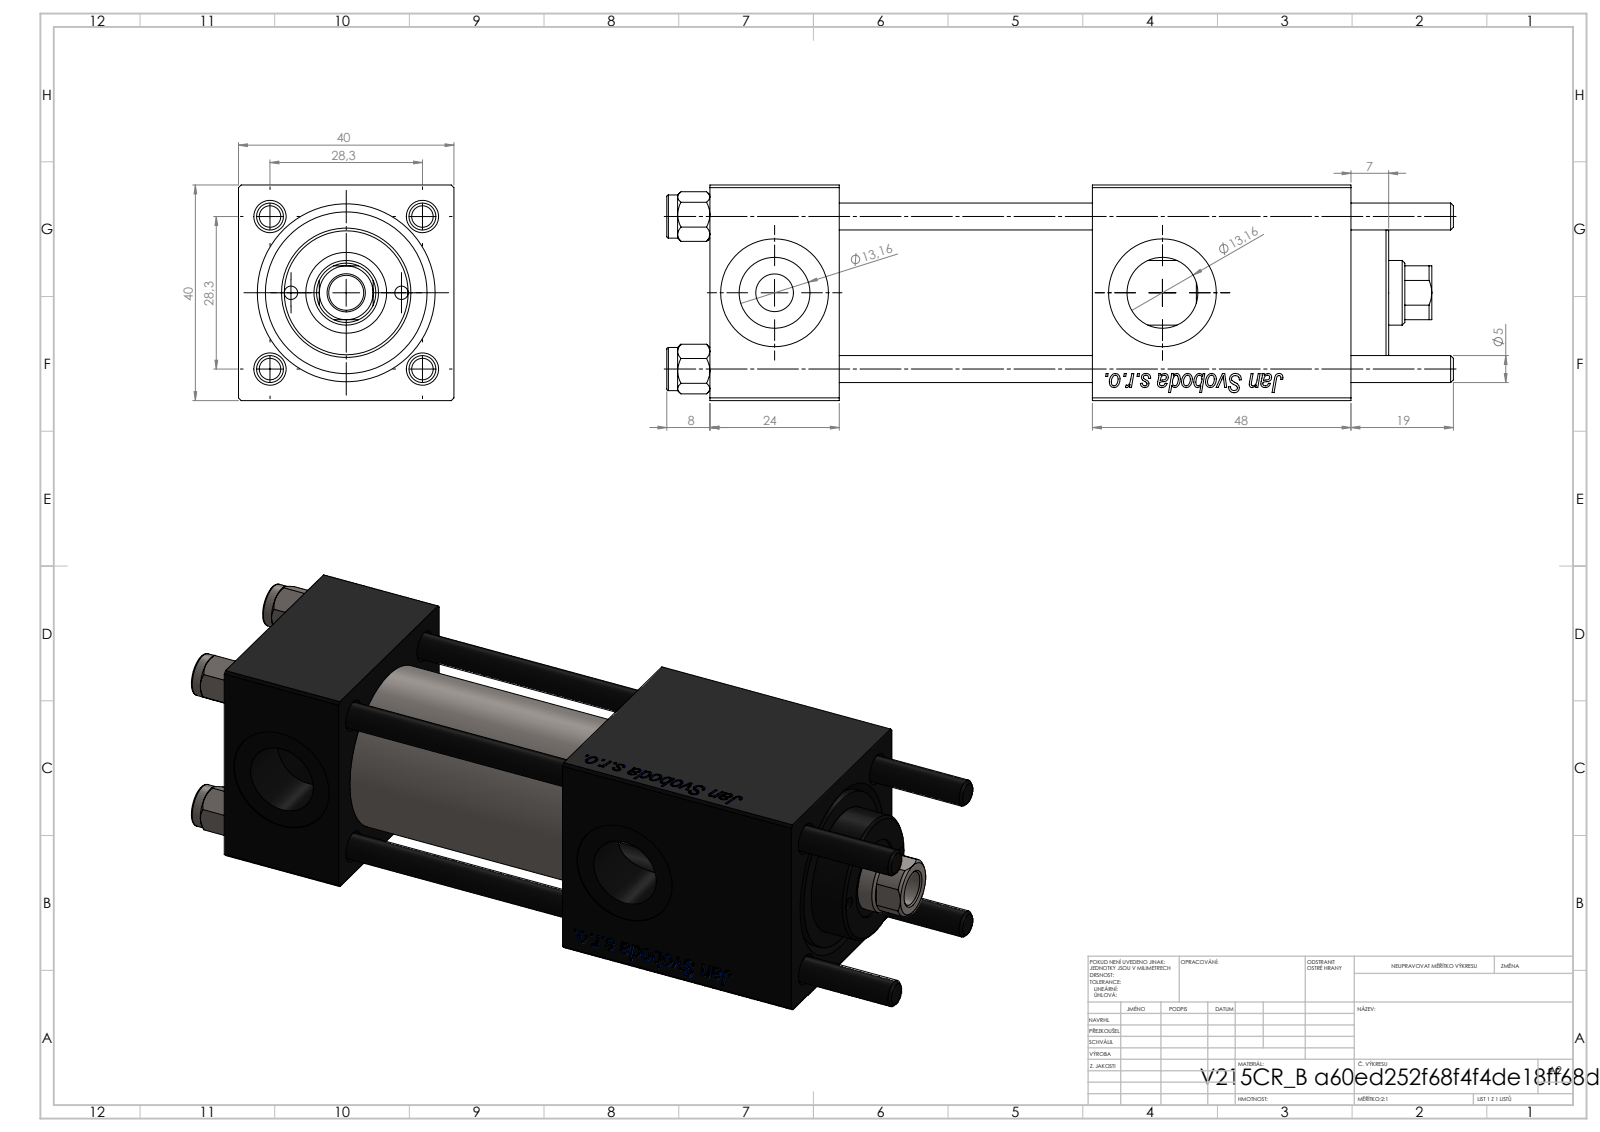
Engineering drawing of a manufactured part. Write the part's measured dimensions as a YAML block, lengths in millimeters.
part_name: "V215CR_B-1; V215_VC_A; V215CR_VCP_B; NUT_M5_B (+1 more)"
step_written_by: "SolidWorks 2019 (CONFIG_CONTROL_DESIGN)"
units: millimeters
bodies: {solids: 11, faces: 1161, planar: 431, cylindrical: 82, other: 648}
overall_size: [146, 40, 40]
volume: 144766
surface_area: 58808
round_holes:
  - {diameter: 5, count: 4}
  - {diameter: 20, count: 3}
  - {diameter: 2.5, count: 2}
  - {diameter: 7, count: 2}
  - {diameter: 13.16, count: 2}
  - {diameter: 6.5, count: 1}
  - {diameter: 12, count: 1}
  - {diameter: 15, count: 1}
  - {diameter: 25, count: 1}
  - {diameter: 30, count: 1}
round_bosses_or_shafts:
  - {diameter: 8, count: 4}
  - {diameter: 31, count: 1}
  - {diameter: 24, count: 1}
partial_cylinders:
  - {radius: 5.5, count: 1}
face_to_face_distances: [40, 24, 90.3, 66.3, 71, 47, 19.3, 119, 95, 48]
hole_center_spacings: [14.68, 20.01, 28.21, 28.3, 10.25, 40.02, 20.5, 72]
